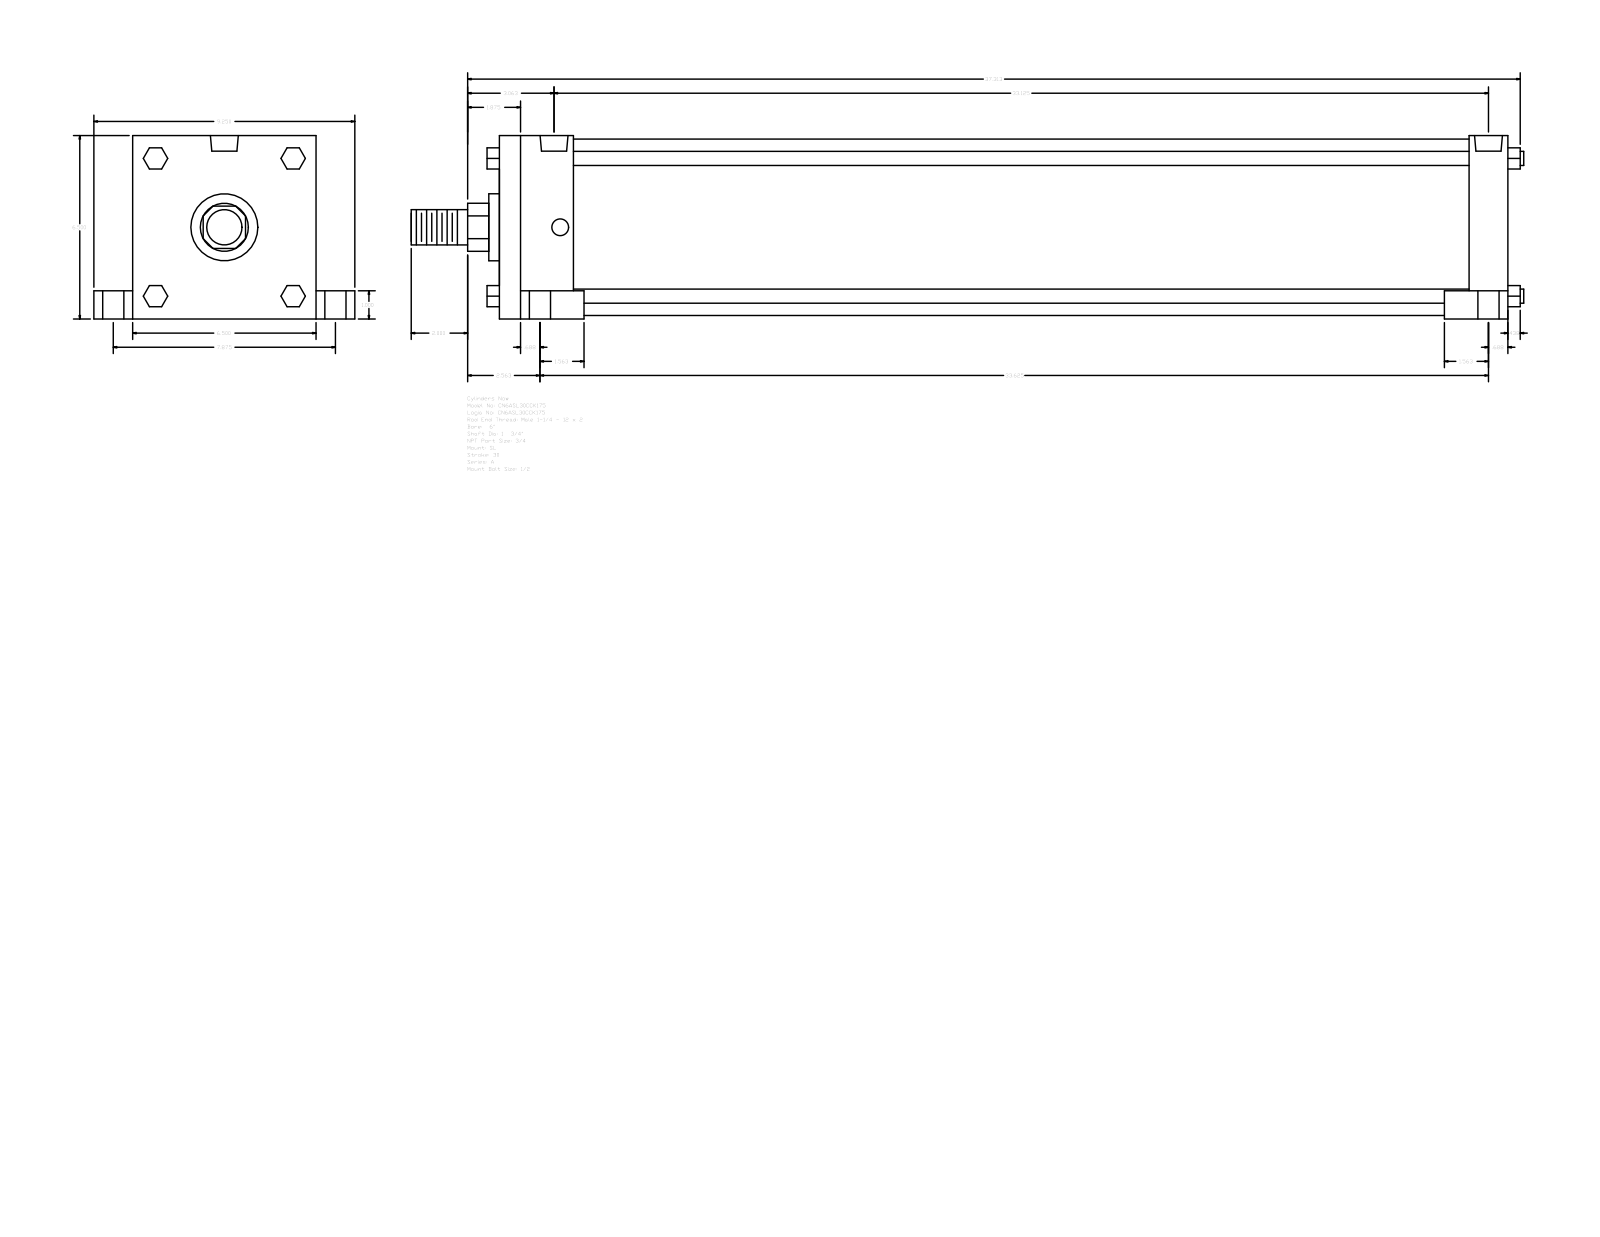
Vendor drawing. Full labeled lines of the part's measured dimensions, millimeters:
Part name (STEP PRODUCT): A_SL__0600_1.75
STEP written by: GSSL Pune (CONFIG_CONTROL_DESIGN)
Units: millimetres
Bodies: 0 solids, 150 faces (114 planar, 36 cylindrical, 0 other)
Overall size (bounding box): 1001.71 × 234.95 × 165.1
Round holes (diameter × count): ⌀15.08 ×4, ⌀19.05 ×4, ⌀25.4 ×4, ⌀25.12 ×2
Round bosses / shafts (diameter × count): ⌀12.7 ×4, ⌀158.75 ×1, ⌀60.33 ×1, ⌀44.45 ×1, ⌀31.75 ×1
Partial cylindrical surfaces — rounded edges, fillets, slot ends (radius × count): R21.63 ×1
Main face-to-face distances: 165.1, 908.05, 34.92, 66.68, 841.37, 873.13, 806.45, 25.4, 139.7, 200.02
Hole centre spacings: 5.56, 100.01, 100.16, 100.81, 101.66, 200.02, 830.25, 835.81
